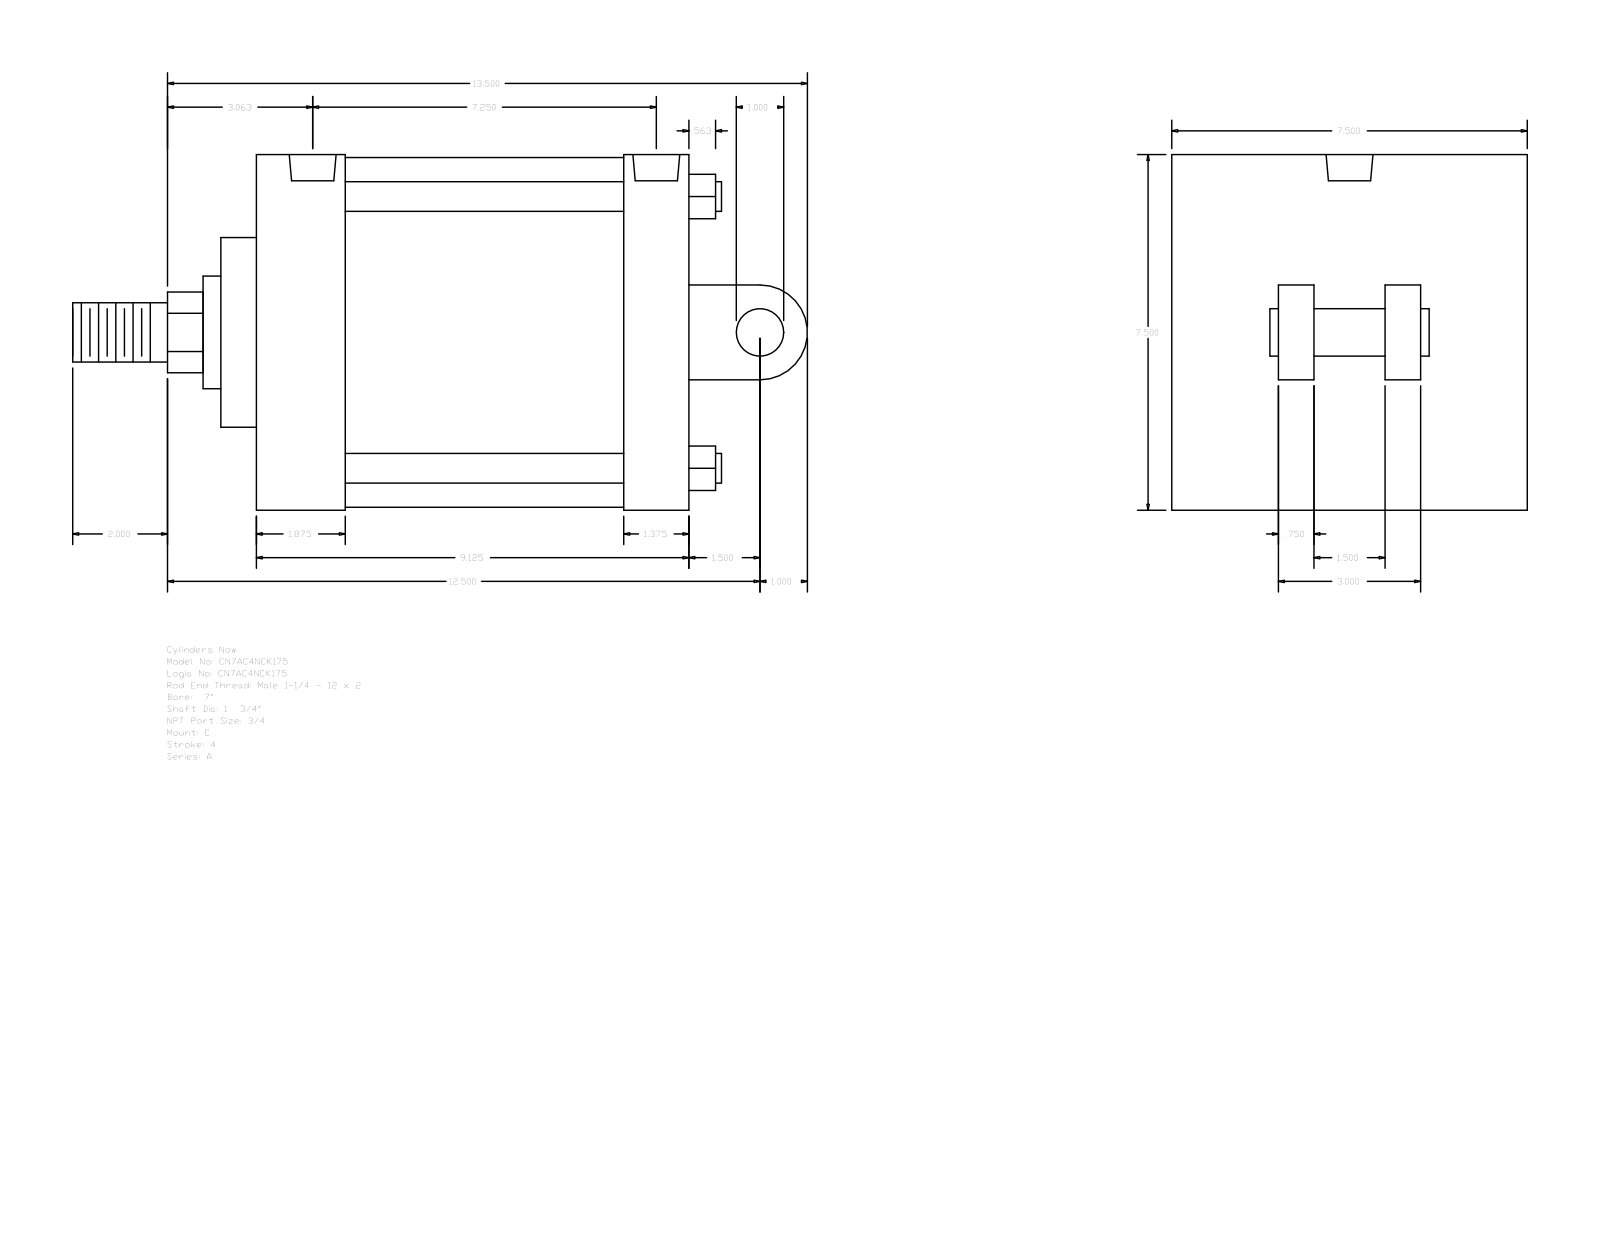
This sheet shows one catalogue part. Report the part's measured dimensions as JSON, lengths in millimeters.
{"part_name": "A_C__0700_1.75", "step_written_by": "GSSL Pune (CONFIG_CONTROL_DESIGN)", "units": "millimeters", "bodies": {"solids": 0, "faces": 104, "planar": 75, "cylindrical": 29, "other": 0}, "overall_size": [393.7, 190.5, 190.5], "round_holes": [[15.08, 4], [25.12, 2]], "round_bosses_or_shafts": [[15.88, 4], [187.32, 1], [60.33, 1], [44.45, 1], [31.75, 1], [25.4, 1]], "partial_cylinders_radius": [[21.63, 1], [25.4, 1]], "face_to_face_distances": [190.5, 231.78, 19.05, 76.2, 57.15, 146.05, 44.45, 69.85, 47.63, 184.15], "hole_center_spacings": [5.56, 173.03, 178.59, 184.15]}
